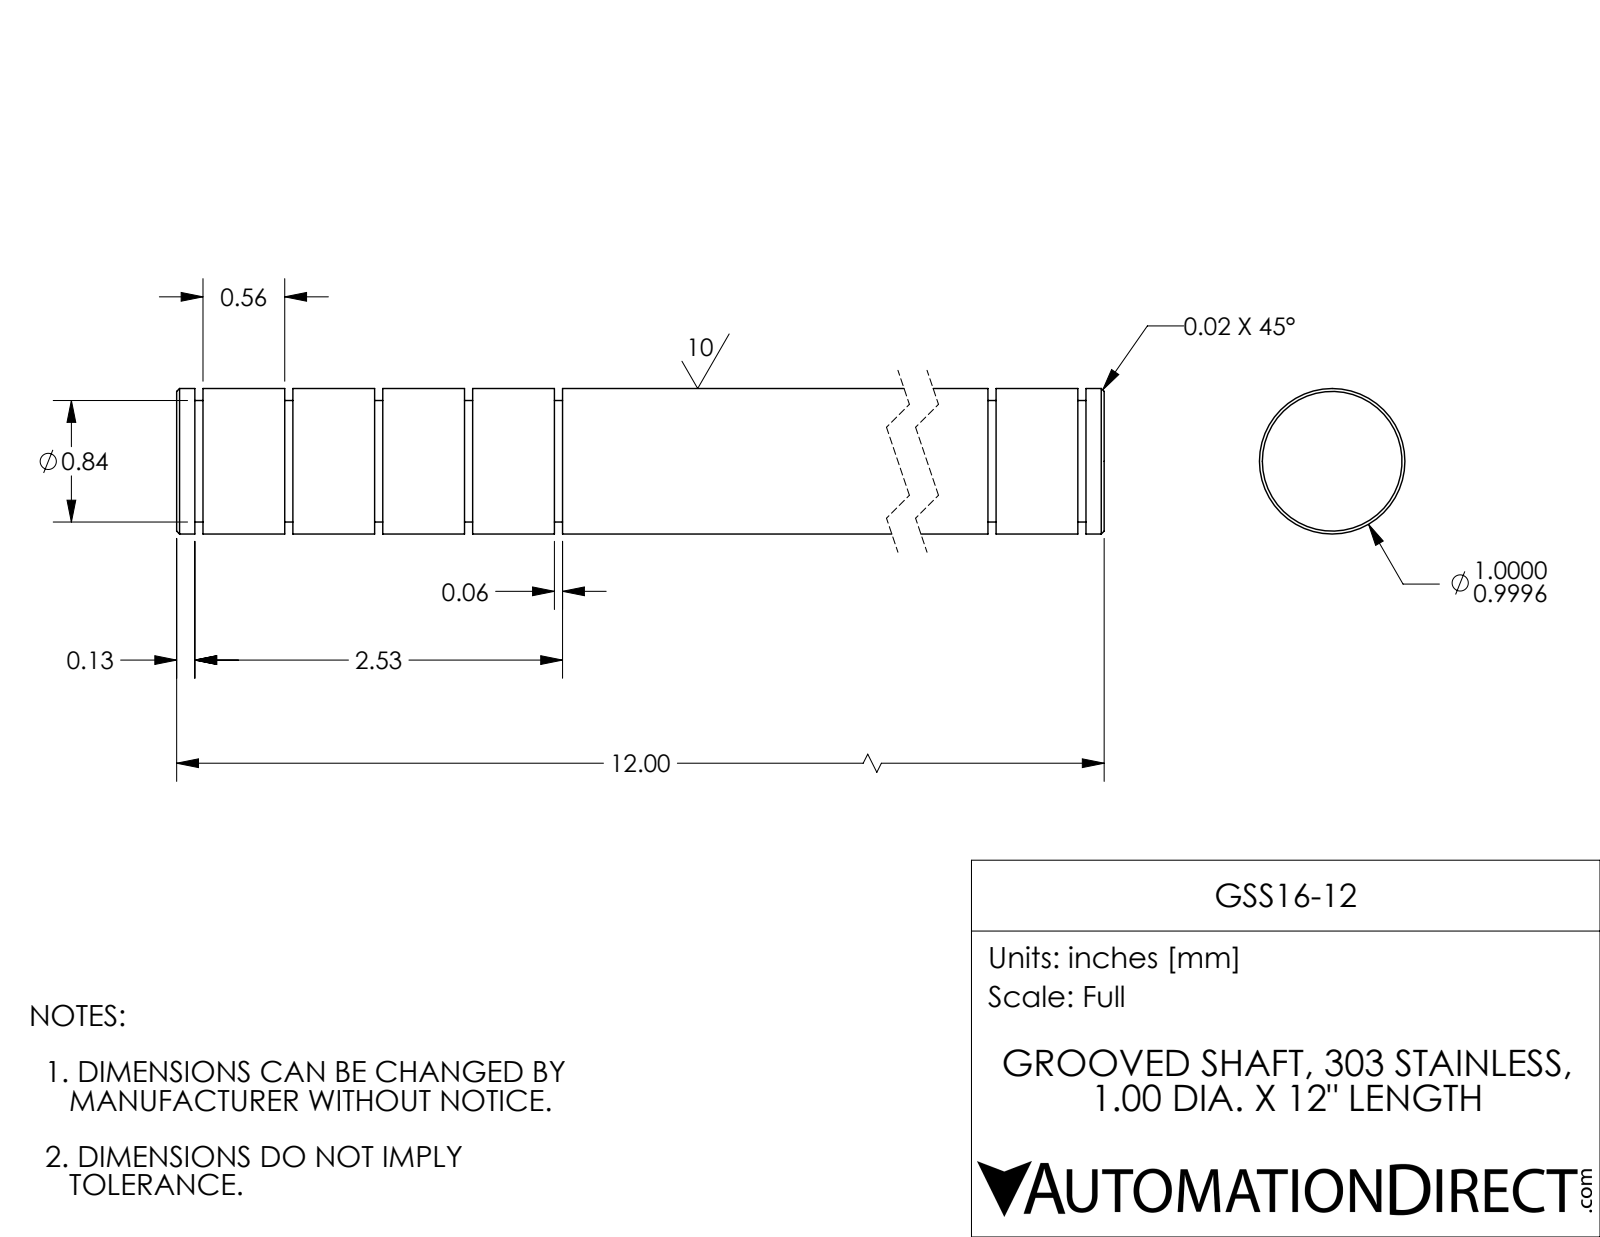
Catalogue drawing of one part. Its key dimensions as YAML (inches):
part_name: "GSS16-12"
step_written_by: "SolidWorks 2017 (AUTOMOTIVE_DESIGN)"
units: inches
bodies: {solids: 1, faces: 50, planar: 16, cylindrical: 30, other: 4}
overall_size: [12, 1, 1]
volume: 9.33
surface_area: 42.32
round_bosses_or_shafts:
  - {diameter: 1, count: 1}
  - {diameter: 0.835, count: 1}
face_to_face_distances: [0.618, 0.056, 0.618, 0.674, 1.236, 12, 9.222, 1.292, 0.562, 11.076]
